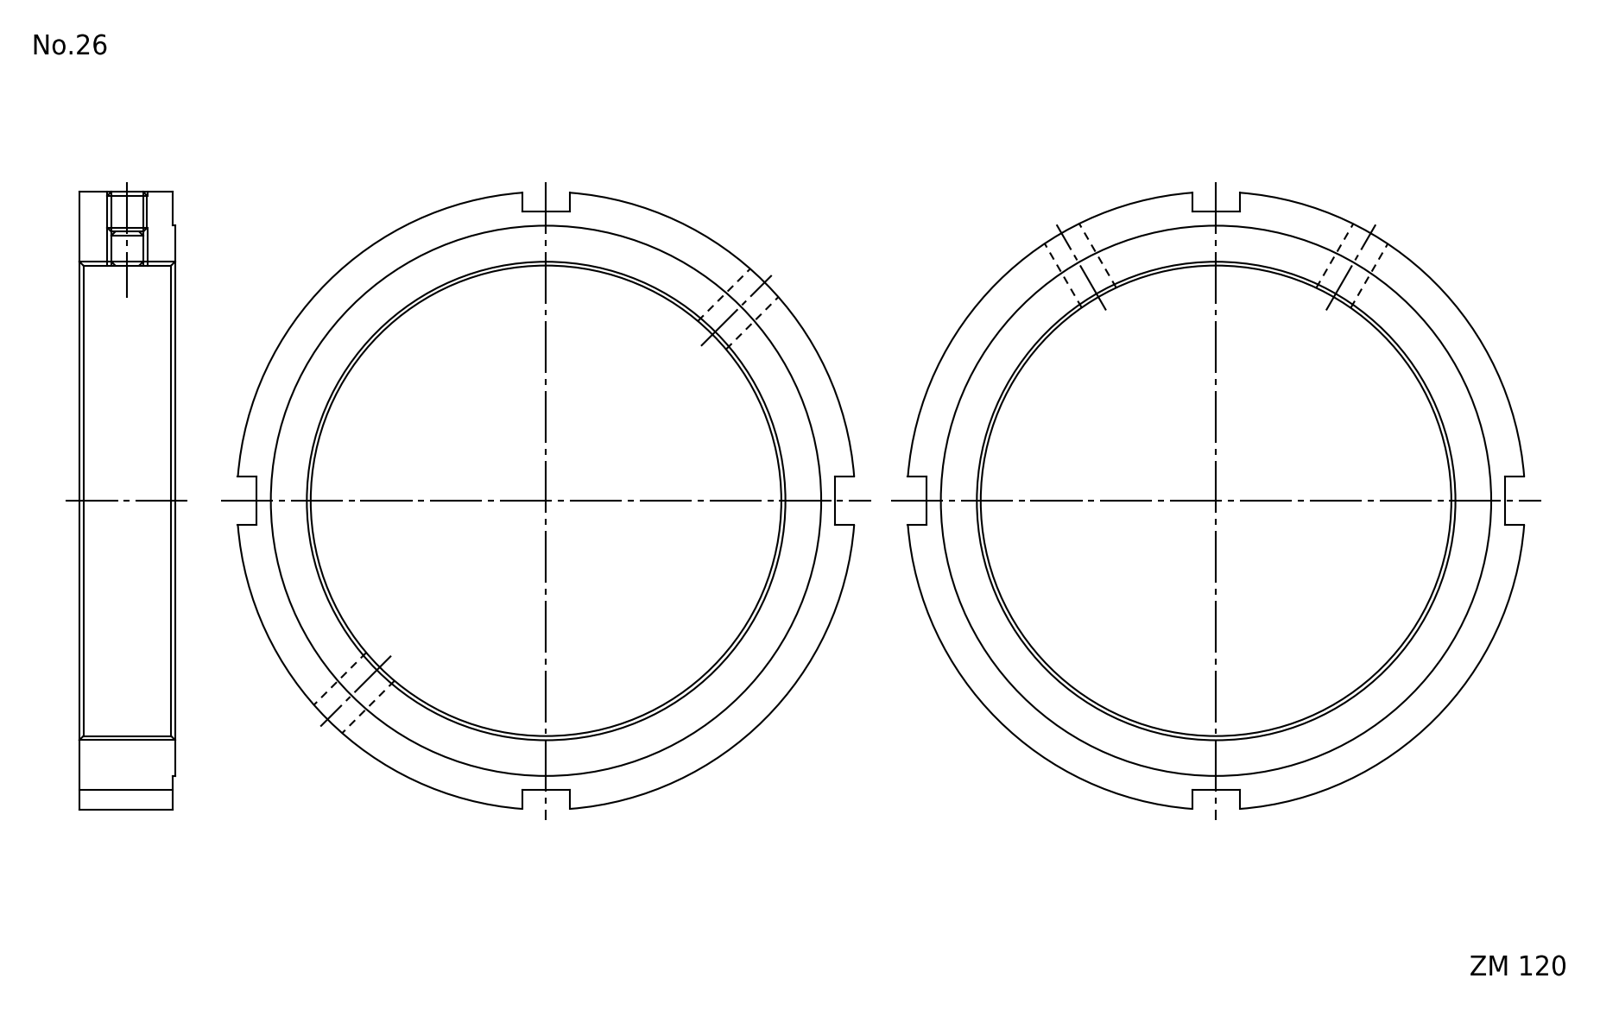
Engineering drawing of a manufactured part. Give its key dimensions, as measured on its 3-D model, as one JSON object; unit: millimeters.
{"part_name": "FKD ZM120", "step_written_by": "Autodesk Inventor 2011 (AUTOMOTIVE_DESIGN)", "units": "millimeters", "bodies": {"solids": 1, "faces": 23, "planar": 15, "cylindrical": 8, "other": 0}, "overall_size": [154.53, 154.53, 24], "volume_mm3": 171990, "surface_area_mm2": 36951, "round_holes": [[8.38, 2], [120, 1]], "round_bosses_or_shafts": [[155, 1], [138, 1]], "face_to_face_distances": [23.5, 0.5, 24, 66.5, 78.5, 145, 12]}
